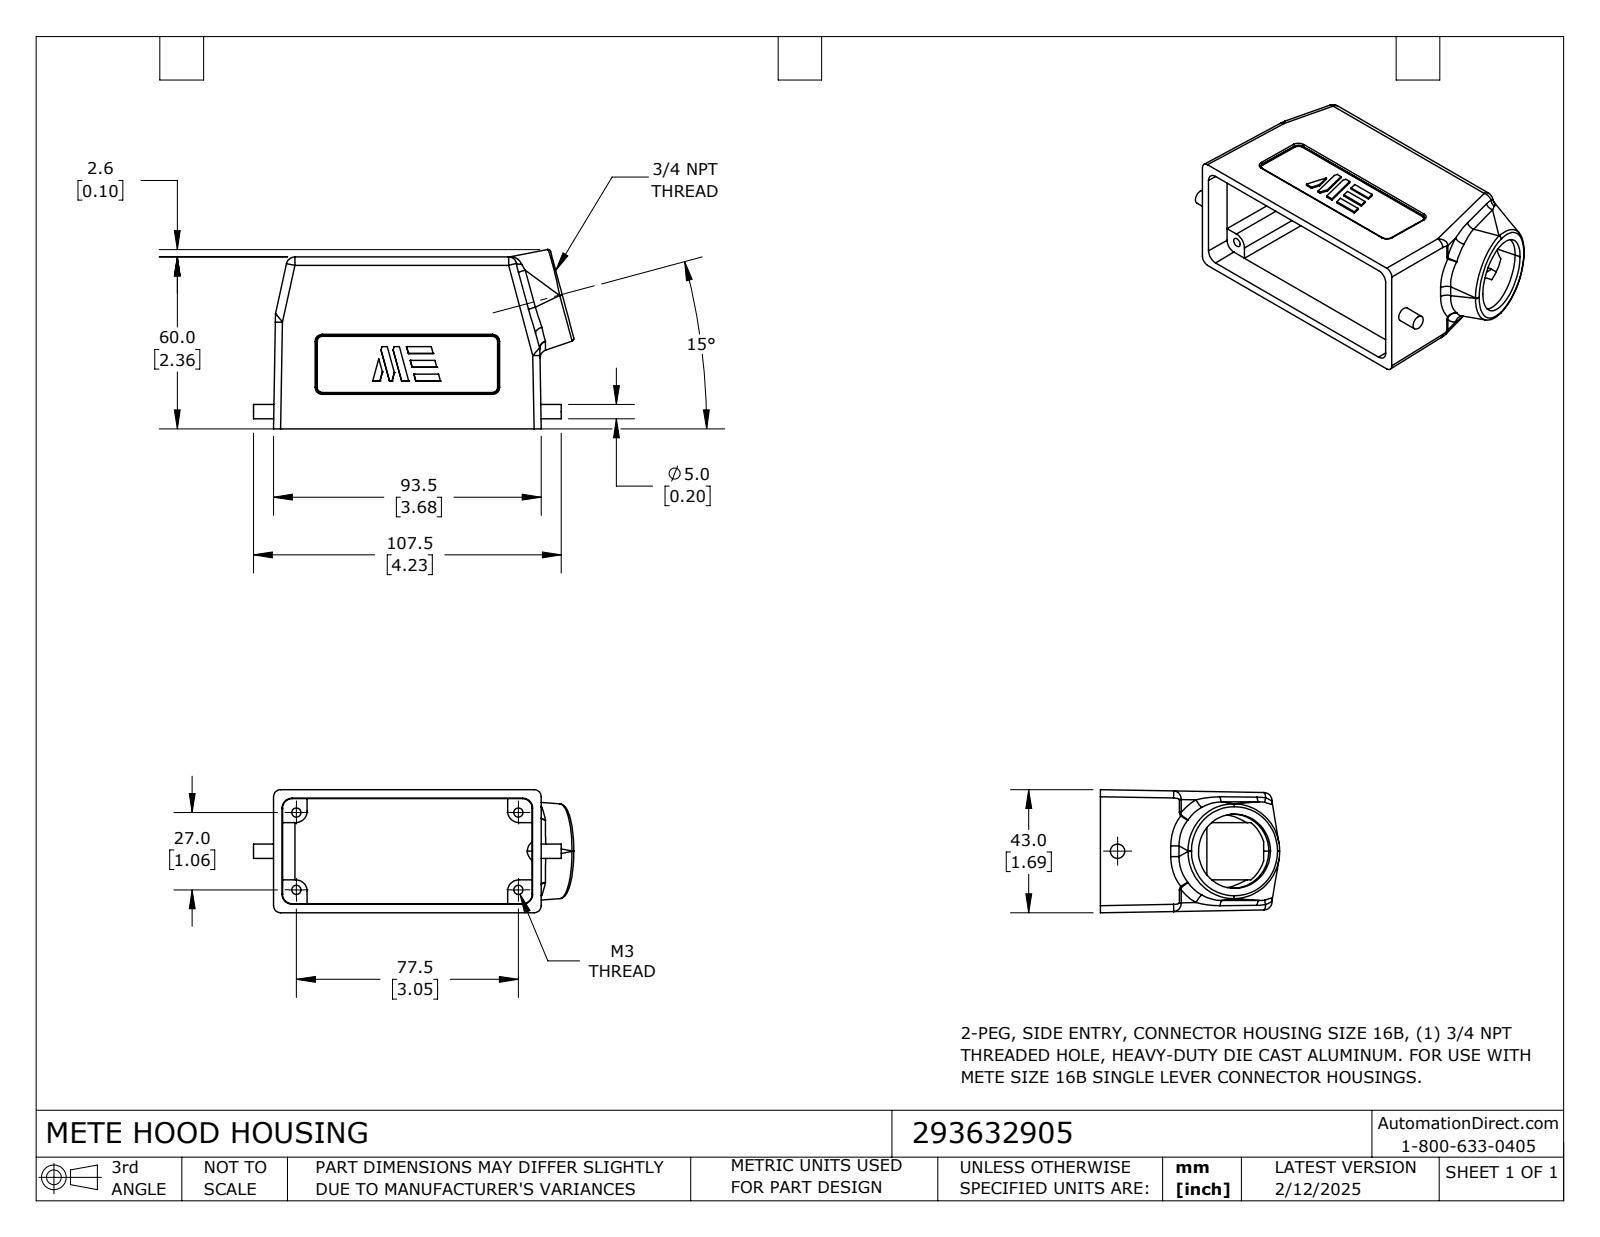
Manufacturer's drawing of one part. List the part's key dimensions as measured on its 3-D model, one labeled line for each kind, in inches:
Part name (STEP PRODUCT): 293632905
STEP written by: SolidWorks 2024 (CONFIG_CONTROL_DESIGN)
Units: inches
Bodies: 1 solid, 245 faces (122 planar, 61 cylindrical, 62 other)
Overall size (bounding box): 4.405 × 2.466 × 1.693
Volume: 3.689 in³ · Surface area: 59.6 in²
Round holes (diameter × count): ⌀0.126 ×4
Round bosses / shafts (diameter × count): ⌀0.197 ×1
Partial cylindrical surfaces — rounded edges, fillets, slot ends (radius × count): R0.118 ×10, R0.008 ×8, R0.02 ×8, R0.079 ×8, R0.098 ×6, R0.157 ×4, R0.039 ×1
Main face-to-face distances: 0.118, 1.444, 0.031, 0.087, 0.338, 3.094, 2.362, 2.244, 0.328, 1.116
Hole centre spacings: 1.063, 3.052, 3.231
